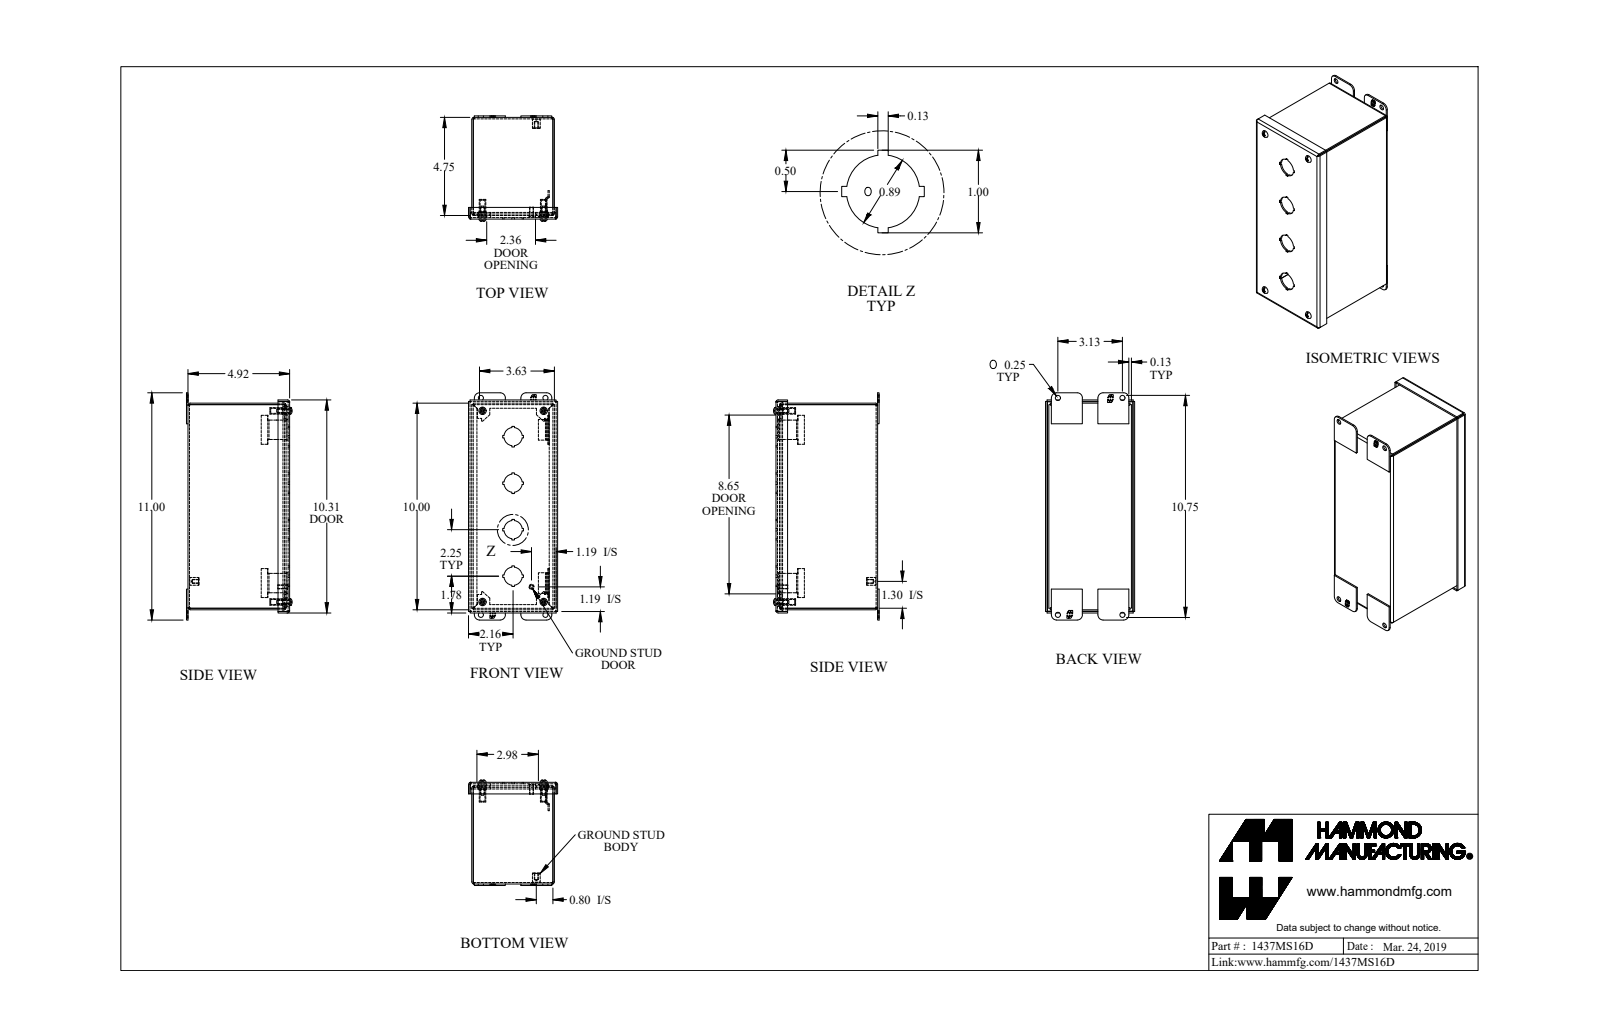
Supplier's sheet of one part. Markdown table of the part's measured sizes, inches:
| quantity | value |
| --- | --- |
| part name | 1437MS16D_Default |
| STEP written by | SolidWorks 2019 (CONFIG_CONTROL_DESIGN) |
| units | inches |
| bodies | 23 solids, 669 faces (471 planar, 168 cylindrical, 30 other) |
| overall size | 11 × 5.104 × 4.312 |
| volume | 20.13 in³ |
| surface area | 537.7 in² |
| round holes (diameter × count) | 0.25 × 8, 0.065 × 4, 0.239 × 4, 0.253 × 4, 0.406 × 4, 0.886 × 4, 0.156 × 1 |
| round bosses / shafts (diameter × count) | 0.19 × 5, 0.406 × 4, 0.315 × 4, 0.148 × 4, 0.375 × 1, 0.25 × 1 |
| partial cylindrical surfaces (radius × count) | 0.036 × 12, 0.108 × 12, 0.25 × 8, 0.029 × 4, 0.086 × 4, 0.171 × 4, 0.125 × 2 |
| main face-to-face distances | 0.072, 3.928, 4.85, 4.922, 4, 3.856, 4.778, 9.928, 0.156, 4.084 |
| hole center spacings | 9.25, 9.875, 10.333, 2.961, 3.107, 9.712, 2.962, 0.63 |
